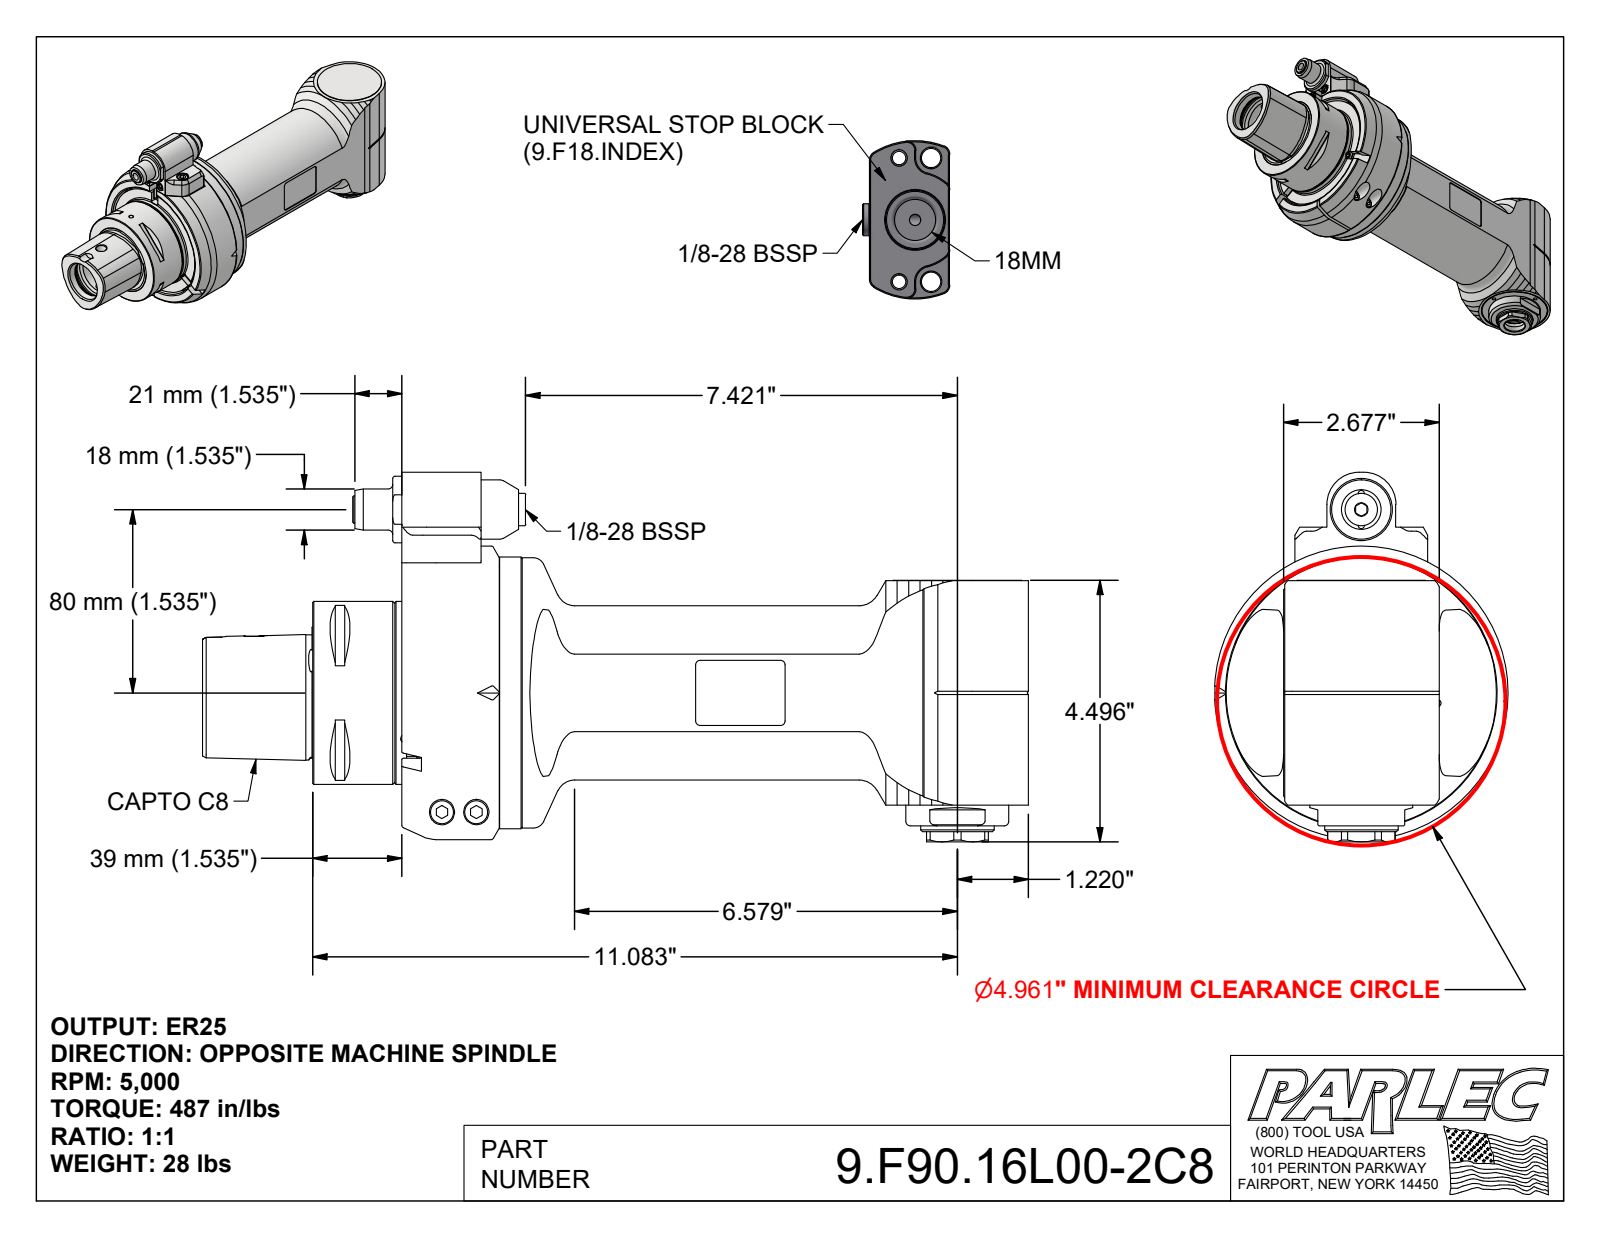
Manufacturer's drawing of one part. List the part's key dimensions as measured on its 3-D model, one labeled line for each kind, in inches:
Part name (STEP PRODUCT): 9.F90.16L00-2C8; 9_F90_16L00
STEP written by: Autodesk Inventor 2025 (AUTOMOTIVE_DESIGN)
Units: inches
Bodies: 5 solids, 592 faces (246 planar, 140 cylindrical, 206 other)
Overall size (bounding box): 14.193 × 6.348 × 5.039
Volume: 123.4 in³ · Surface area: 335.4 in²
Round holes (diameter × count): ⌀0.413 ×20, ⌀0.126 ×4, ⌀0.197 ×4, ⌀0.102 ×2, ⌀0.165 ×2, ⌀0.209 ×2, ⌀0.315 ×2, ⌀0.409 ×2, ⌀0.433 ×2, ⌀0.492 ×2, ⌀0.709 ×2, ⌀0.098 ×1
Round bosses / shafts (diameter × count): ⌀0.394 ×4, ⌀0.236 ×4, ⌀0.098 ×2, ⌀5.039 ×1, ⌀4.669 ×1, ⌀4.646 ×1, ⌀3.898 ×1, ⌀3.15 ×1
Partial cylindrical surfaces — rounded edges, fillets, slot ends (radius × count): R0.079 ×12, R0.157 ×4, R0.016 ×2, R0.02 ×2, R0.039 ×2, R0.315 ×2, R0.551 ×2, R0.236 ×1
Main face-to-face distances: 0.02, 1.398, 0.039, 1.378, 0.079, 2.677, 0.256, 1.28, 1.339, 0.059
Hole centre spacings: 1.841, 3.645, 1.785, 2.603, 2.94, 2.215, 3.22, 1.015
